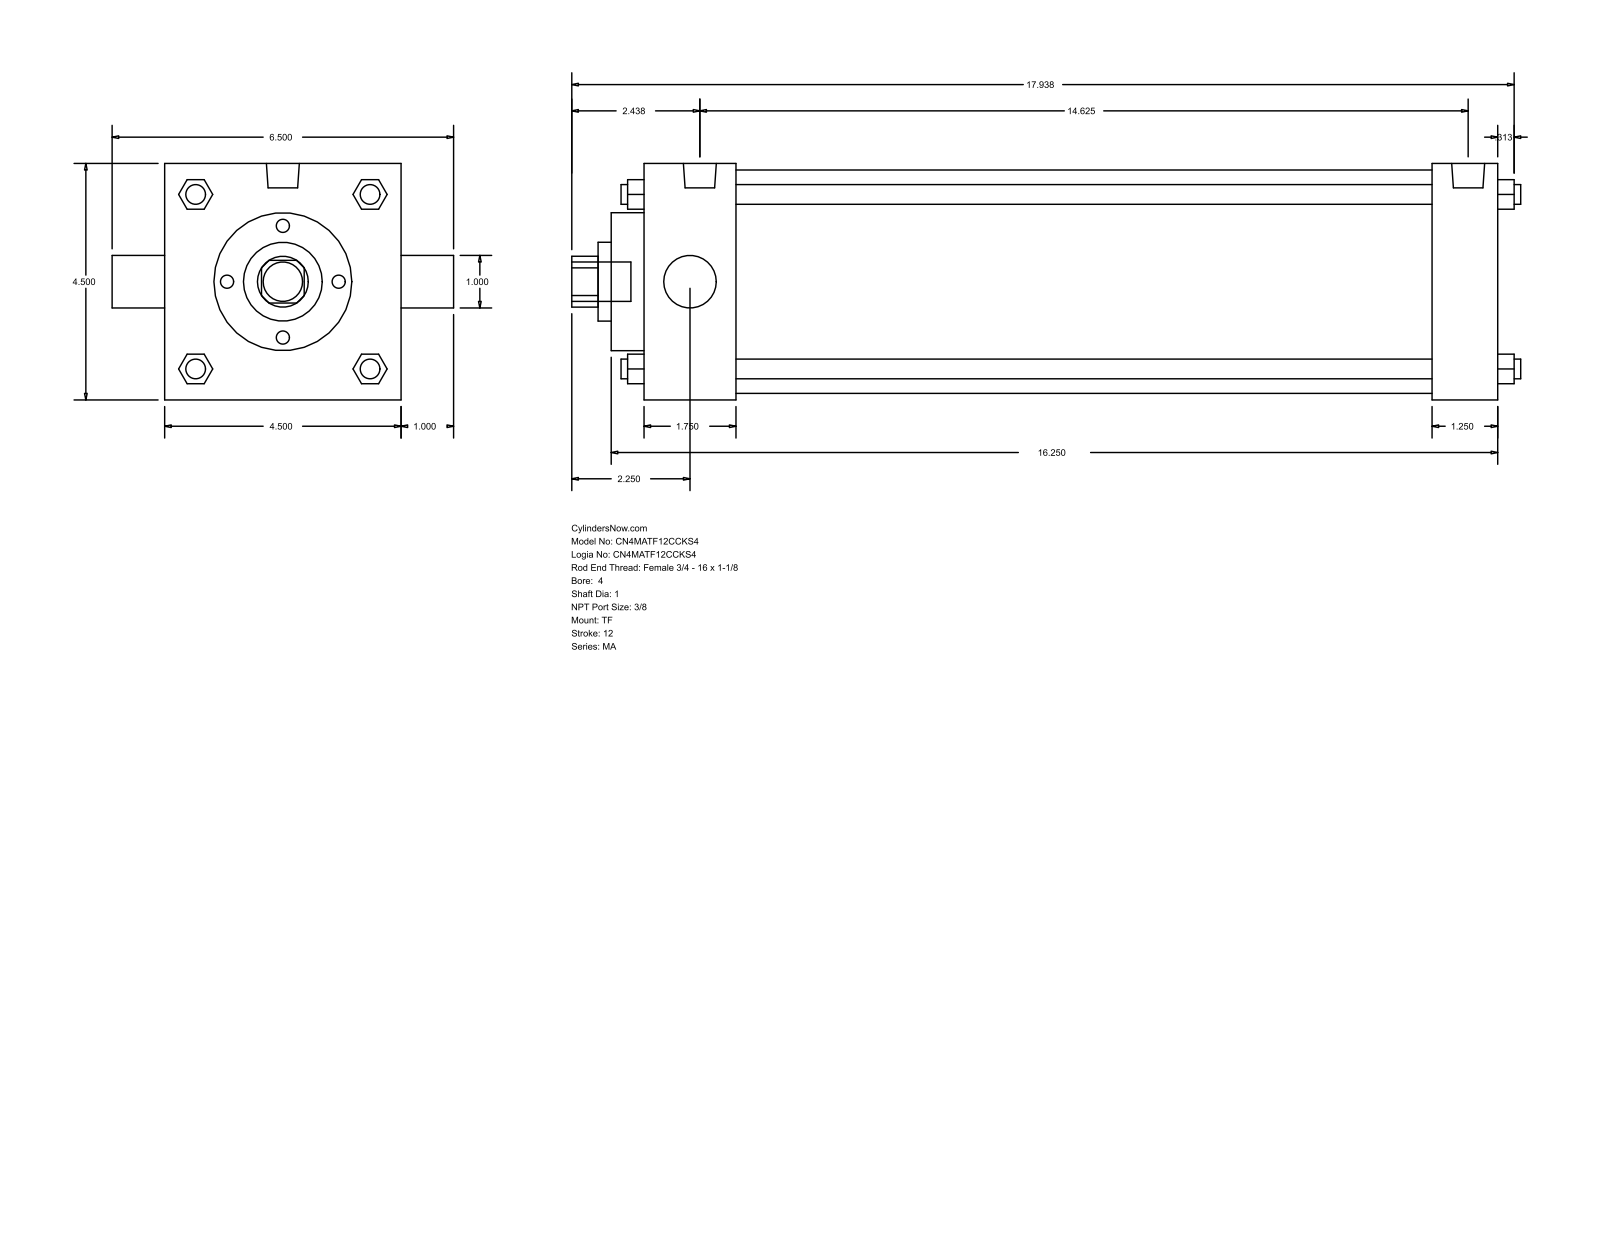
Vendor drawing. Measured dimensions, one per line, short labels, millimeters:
name: MA_TF__0400_1
written by: GSSL Pune (CONFIG_CONTROL_DESIGN)
unit: mm
bodies: 0 solids, 122 faces (93 planar, 29 cylindrical, 0 other)
size: 458.79 × 165.1 × 114.3
holes: 2× ⌀25.4, 1× ⌀38.1, 1× ⌀66.67, 1× ⌀107.95
bosses: 4× ⌀9.53, 3× ⌀11.11, 2× ⌀15.93, 1× ⌀19.05
rounds: 1× R12.29
face distances: 114.3, 412.76, 381.01, 31.75, 44.46, 336.55, 368.3, 15.87, 60.33, 396.88
